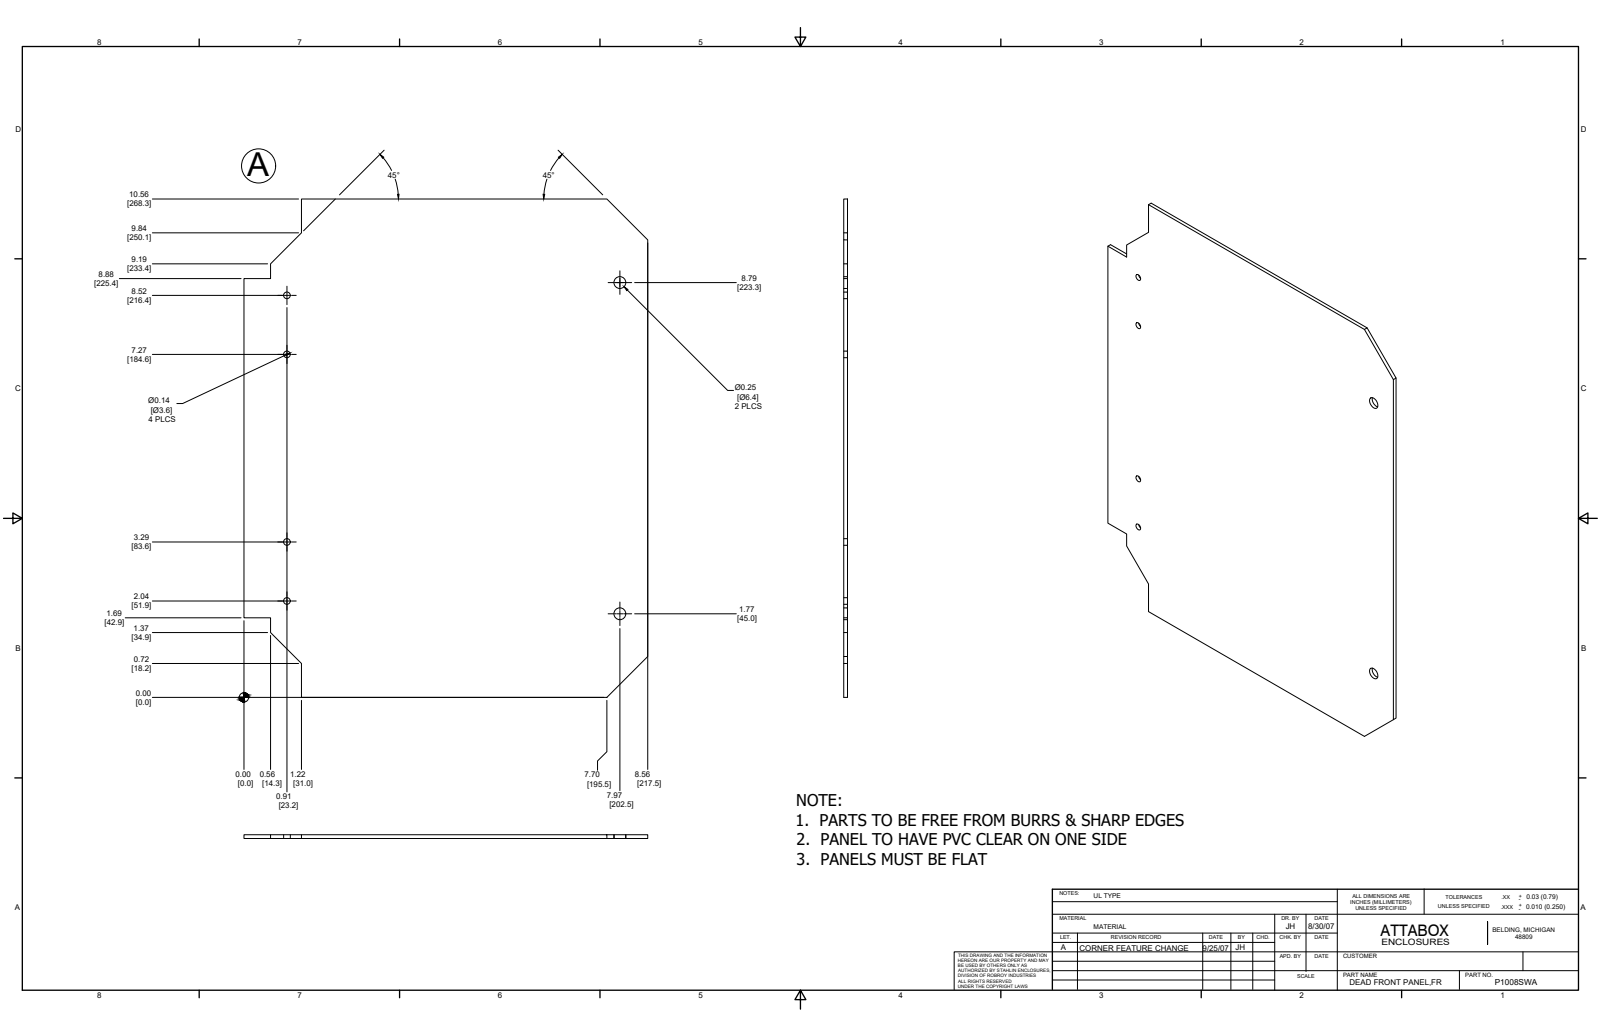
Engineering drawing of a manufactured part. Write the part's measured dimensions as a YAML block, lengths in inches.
part_name: "P1008SWAL"
step_written_by: "Autodesk Inventor 11 (AUTOMOTIVE_DESIGN)"
units: inches
bodies: {solids: 1, faces: 20, planar: 14, cylindrical: 6, other: 0}
overall_size: [10.563, 8.563, 0.08]
volume: 6.987
surface_area: 177.9
round_holes:
  - {diameter: 0.14, count: 4}
  - {diameter: 0.25, count: 2}
face_to_face_distances: [0.08, 8.562, 10.562, 1.09, 9.472, 7.472, 11.671, 8.383]
hole_center_spacings: [1.25, 5.226, 7.065, 7.222, 8.948, 9.766, 3.976, 6.476]
